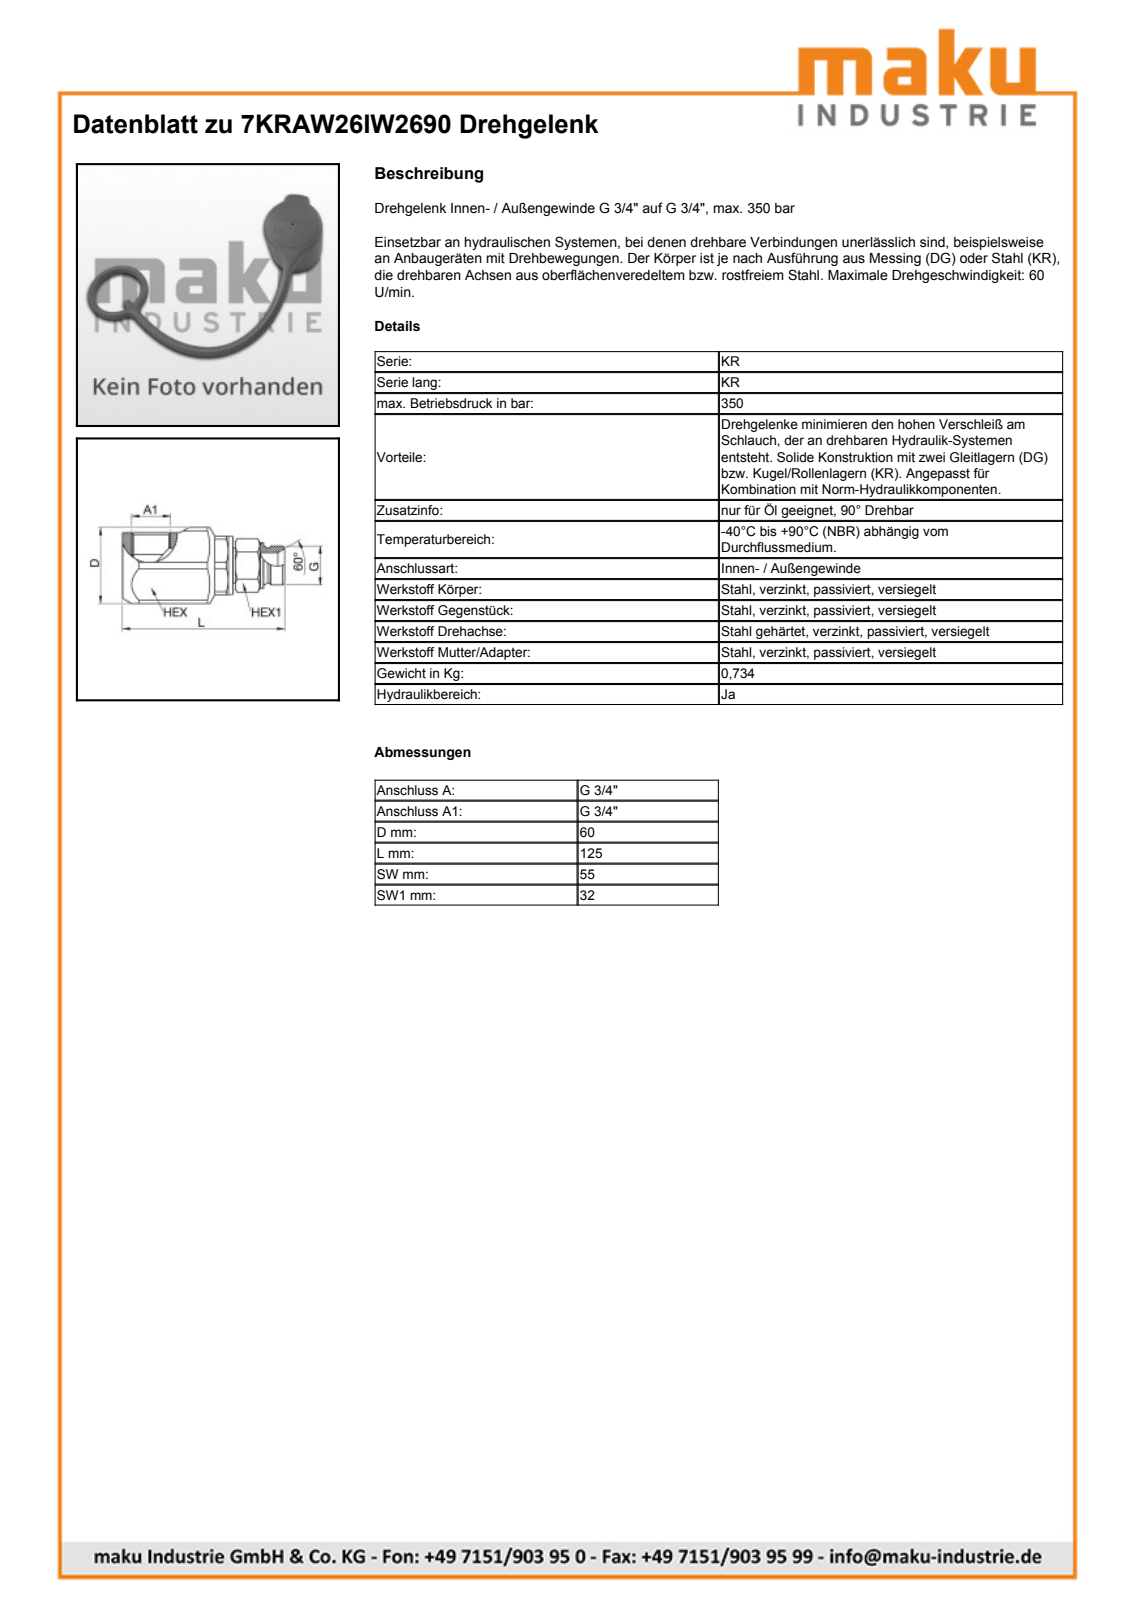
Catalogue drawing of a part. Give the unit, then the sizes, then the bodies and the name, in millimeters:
Units: millimetres
Overall size (bounding box): 123.7 × 60 × 55
Round holes (diameter × count): ⌀17 ×1, ⌀20.2 ×1, ⌀24.12 ×1, ⌀25 ×1, ⌀32 ×1
Round bosses / shafts (diameter × count): ⌀44.7 ×1, ⌀26.44 ×1, ⌀24.9 ×1, ⌀24 ×1
Partial cylindrical surfaces — rounded edges, fillets, slot ends (radius × count): R24.5 ×1, R30 ×1
Main face-to-face distances: 55, 5, 50, 32, 52, 85.7, 45, 3, 87.2, 1.5
Volume: 187 582 mm³ · Surface area: 31 139 mm²
Bodies: 1 solid, 136 faces (32 planar, 35 cylindrical, 69 other)
Part name (STEP PRODUCT): 7KRAW26IW2690
STEP written by: SolidWorks 2009 (AUTOMOTIVE_DESIGN)
